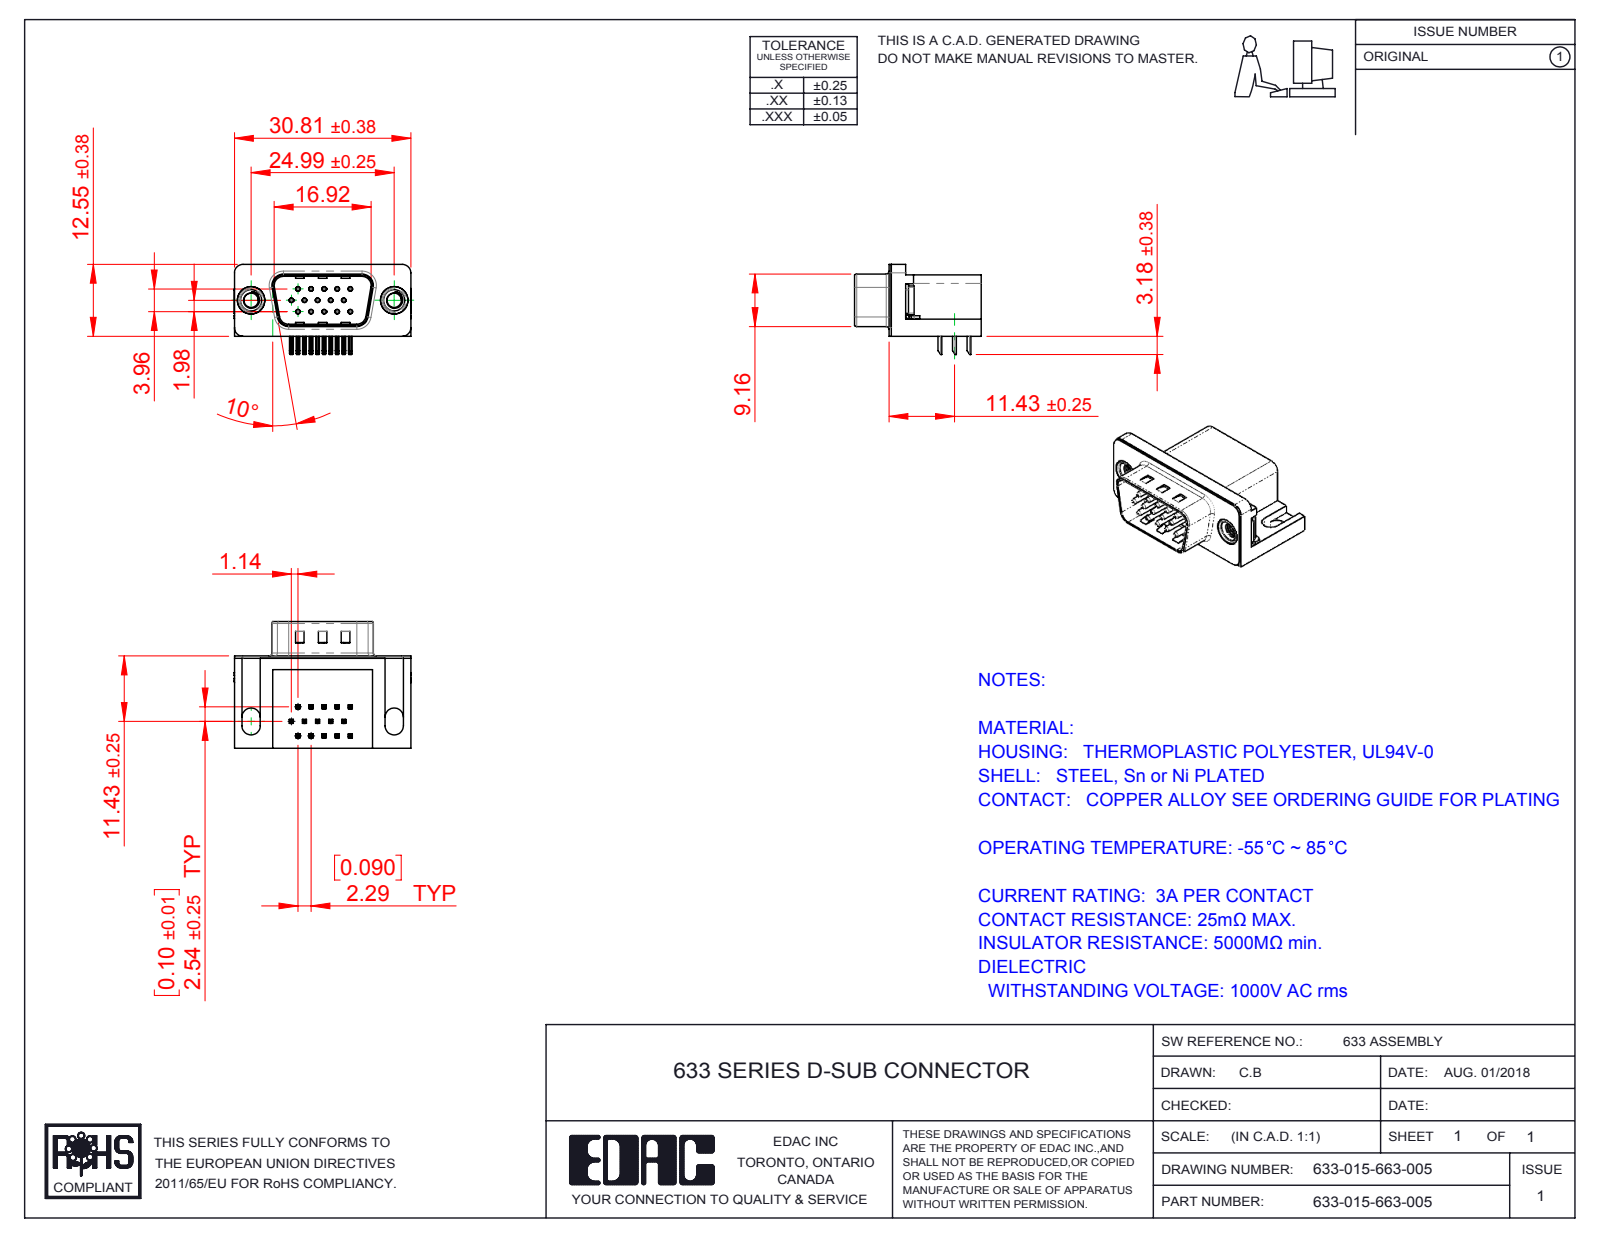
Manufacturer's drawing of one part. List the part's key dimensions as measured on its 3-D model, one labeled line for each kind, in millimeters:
Part name (STEP PRODUCT): 633 Non Board Mount; 633 Contact Middle; 633 M3 Threaded Rivet; 633 Shell_15 Contact (+4 more)
STEP written by: SolidWorks 2016 (CONFIG_CONTROL_DESIGN)
Units: millimetres
Bodies: 21 solids, 1439 faces (861 planar, 443 cylindrical, 135 other)
Overall size (bounding box): 30.89 × 22.1 × 15.73
Volume: 4 020 mm³ · Surface area: 5 205 mm²
Round holes (diameter × count): ⌀0.35 ×15, ⌀0.8 ×15, ⌀2.5 ×2, ⌀4 ×2, ⌀4.8 ×2, ⌀5 ×2
Round bosses / shafts (diameter × count): ⌀0.75 ×15, ⌀4.9 ×2, ⌀4.75 ×2, ⌀3.9 ×2
Partial cylindrical surfaces — rounded edges, fillets, slot ends (radius × count): R0.25 ×68, R0.12 ×30, R1 ×16, R0.5 ×9, R1.6 ×8, R1.5 ×7, R0.9 ×4, R2 ×4
Main face-to-face distances: 0.4, 10.35, 15.7, 2.9, 6.7, 16.1, 2.5, 0.35, 10.7, 13.2
Hole centre spacings: 3.96, 2.28, 4.57, 2.29, 6.05, 6.86, 7.92, 6.04
